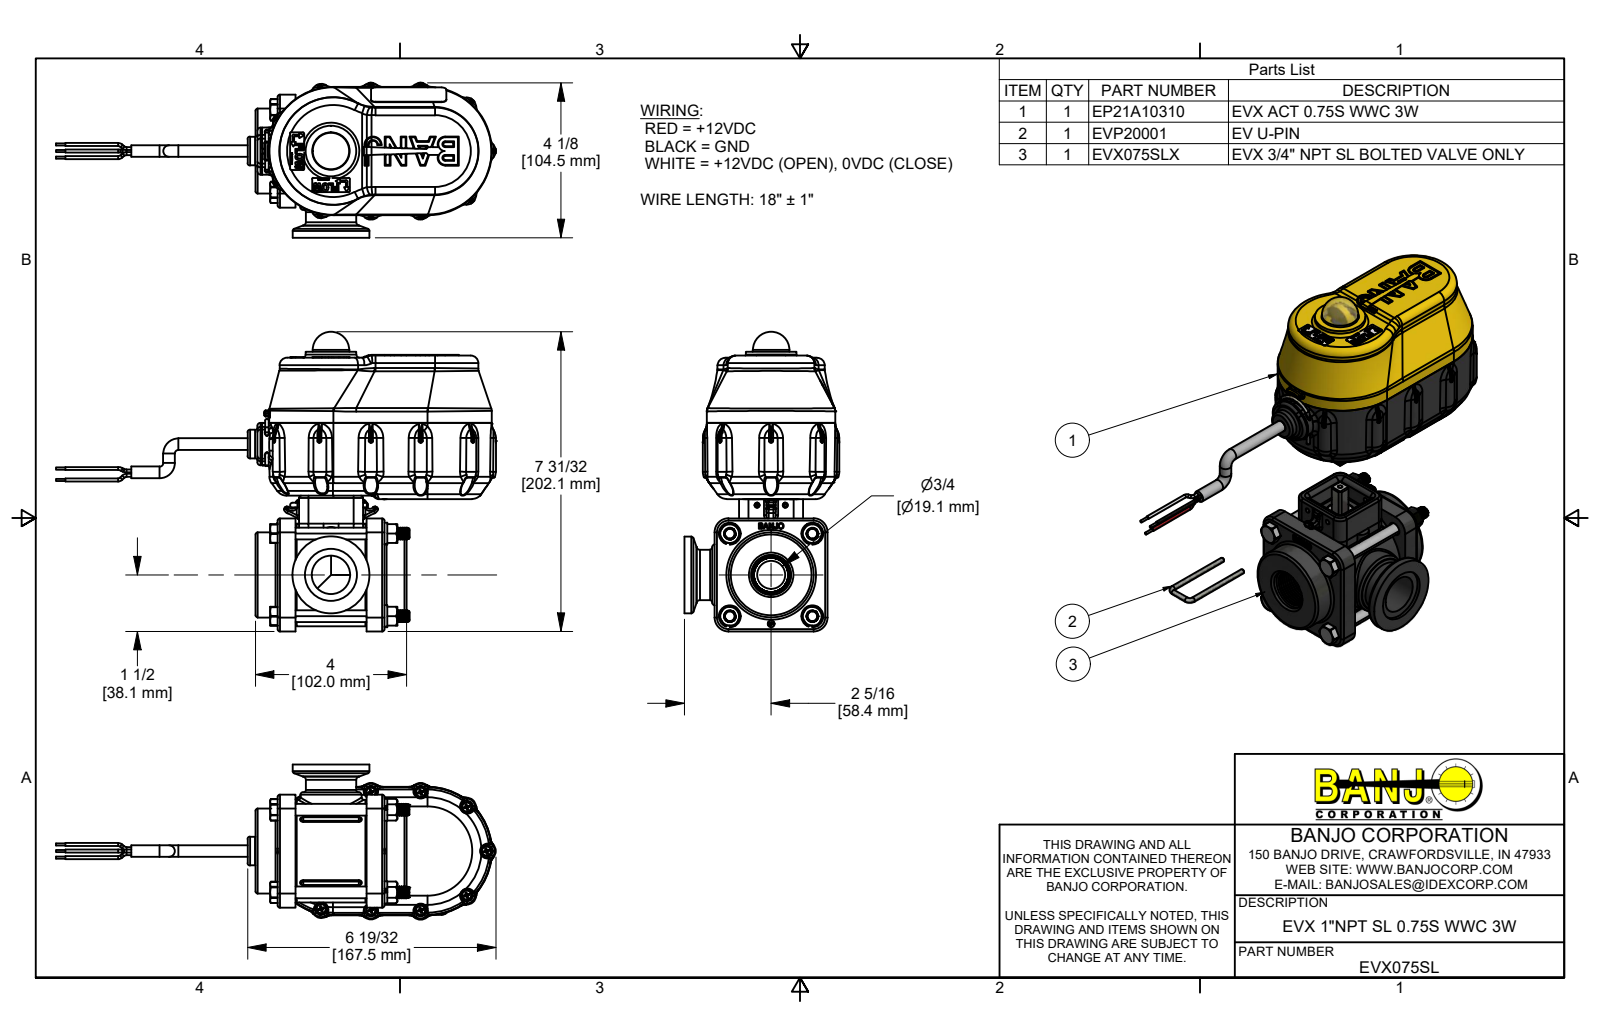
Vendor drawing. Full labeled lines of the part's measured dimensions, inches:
Part name (STEP PRODUCT): EVX075SL; EP21A10310; EP10310; IRF4905 (+8 more)
STEP written by: Autodesk Inventor 2019 (AUTOMOTIVE_DESIGN)
Units: inches
Bodies: 98 solids, 12141 faces (3306 planar, 3485 cylindrical, 5350 other)
Overall size (bounding box): 11.685 × 7.957 × 4.115
Volume: 53.99 in³ · Surface area: 593.5 in²
Round holes (diameter × count): ⌀0.095 ×11, ⌀0.15 ×11, ⌀0.08 ×7, ⌀0.107 ×4, ⌀0.126 ×4, ⌀0.136 ×4, ⌀0.148 ×4, ⌀0.15 ×4, ⌀0.17 ×4, ⌀0.252 ×4, ⌀0.322 ×4, ⌀0.365 ×4
Round bosses / shafts (diameter × count): ⌀0.268 ×60, ⌀0.25 ×17, ⌀0.08 ×15, ⌀0.14 ×11, ⌀0.108 ×11, ⌀0.085 ×11, ⌀0.058 ×6, ⌀0.313 ×5
Partial cylindrical surfaces — rounded edges, fillets, slot ends (radius × count): R0.013 ×180, R0.04 ×145, R0.01 ×84, R0.02 ×72, R0.06 ×58, R0.005 ×53, R0.03 ×38, R0.08 ×28
Main face-to-face distances: 0.1, 2.565, 0.055, 0.211, 0.06, 0.151, 2.36, 0.475, 2.95, 0.125
Hole centre spacings: 1.55, 2.192, 2.656, 1.046, 1.513, 1.662, 1.891, 2.69
